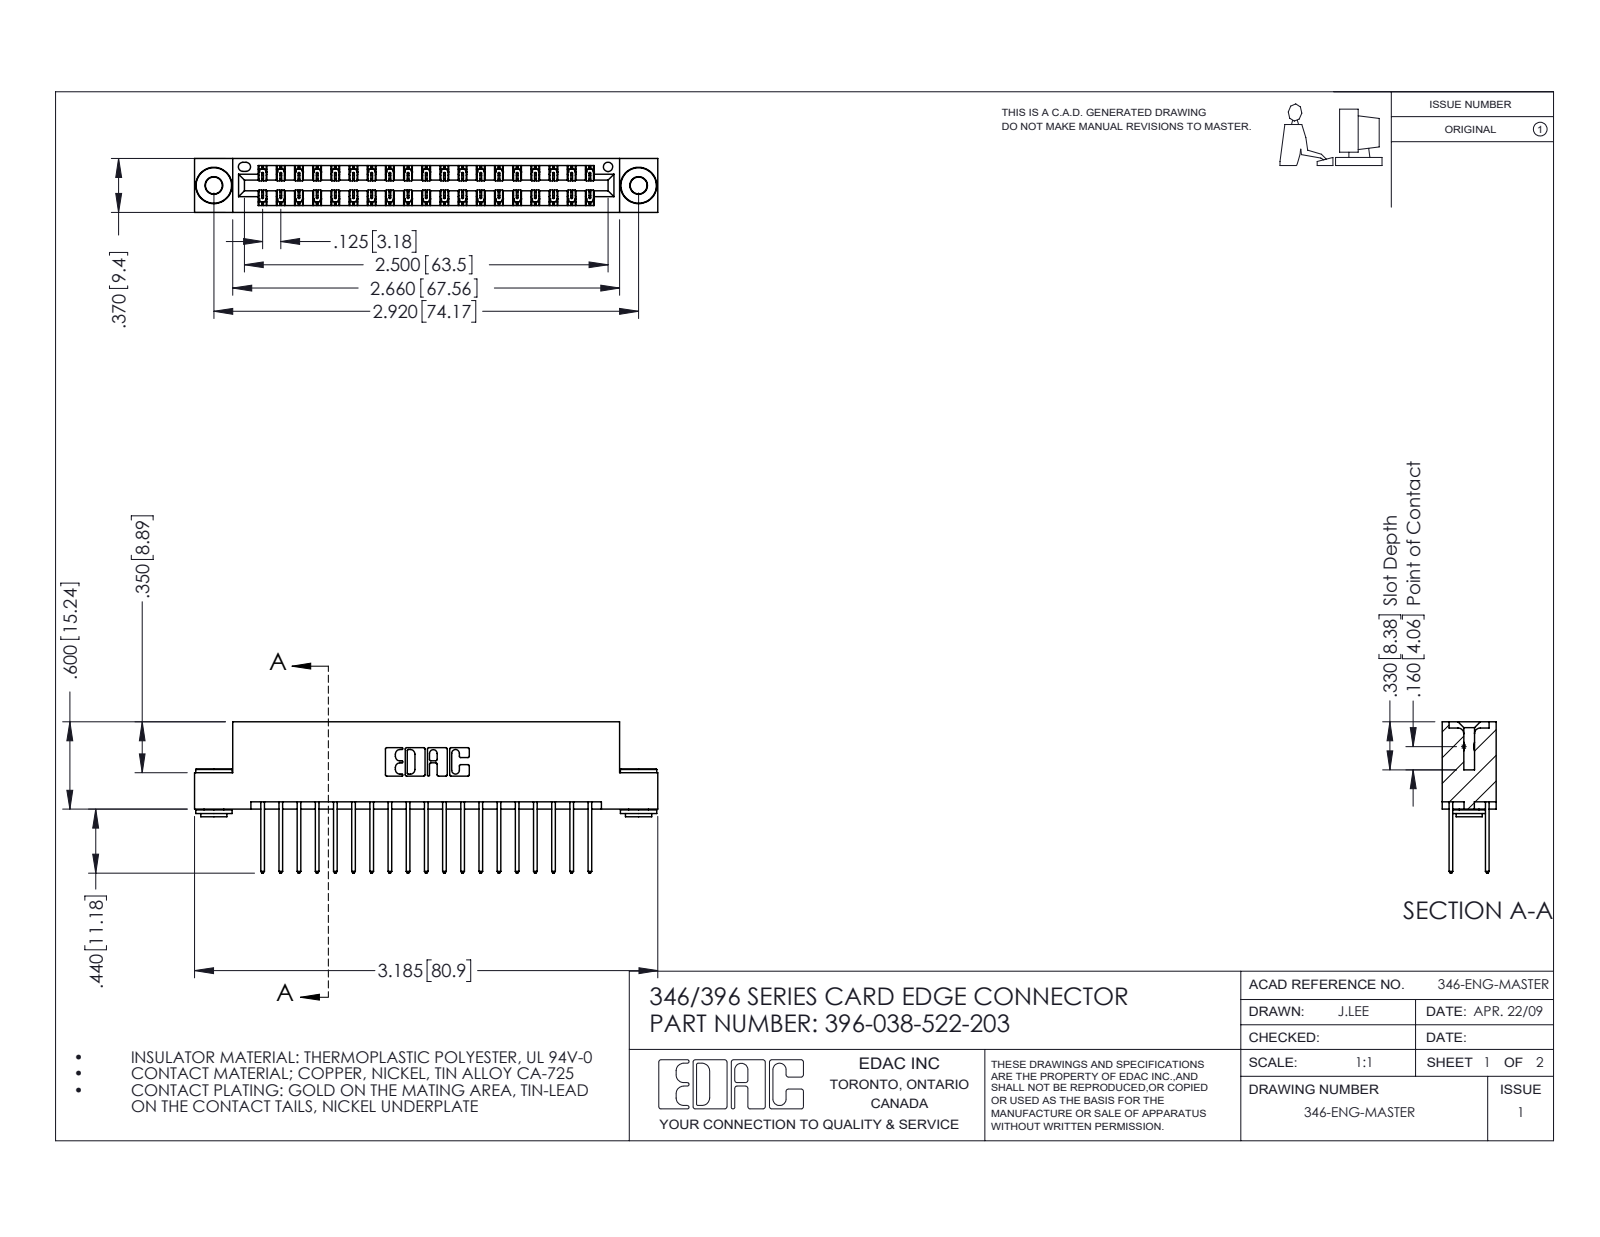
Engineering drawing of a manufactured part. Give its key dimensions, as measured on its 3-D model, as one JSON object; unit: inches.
{"part_name": "346 Part_Flush Mounting Lugs - 0.156 Dia-TH; 345-250-002_345-250-002-102; 345-292-001_345-293-122; 396-038-522-203", "step_written_by": "SolidWorks 2016 (CONFIG_CONTROL_DESIGN)", "units": "inches", "bodies": {"solids": 41, "faces": 2136, "planar": 1416, "cylindrical": 712, "other": 8}, "overall_size": [3.185, 1.04, 0.37], "volume_in3": 0.478, "surface_area_in2": 17.15, "round_holes": [[0.116, 2], [0.156, 2], [0.064, 1]], "round_bosses_or_shafts": [[0.25, 2], [0.18, 2], [0.136, 2]], "partial_cylinders_radius": [[0.006, 57], [0.01, 38], [0.01, 22], [0.007, 6], [0.031, 6], [0.026, 3], [0.014, 2], [0.022, 2]], "face_to_face_distances": [0.048, 0.322, 0.25, 0.37, 0.025, 0.072, 0.298, 0.275, 0.148, 0.222], "hole_center_spacings": [0.246, 2.713, 2.92]}
